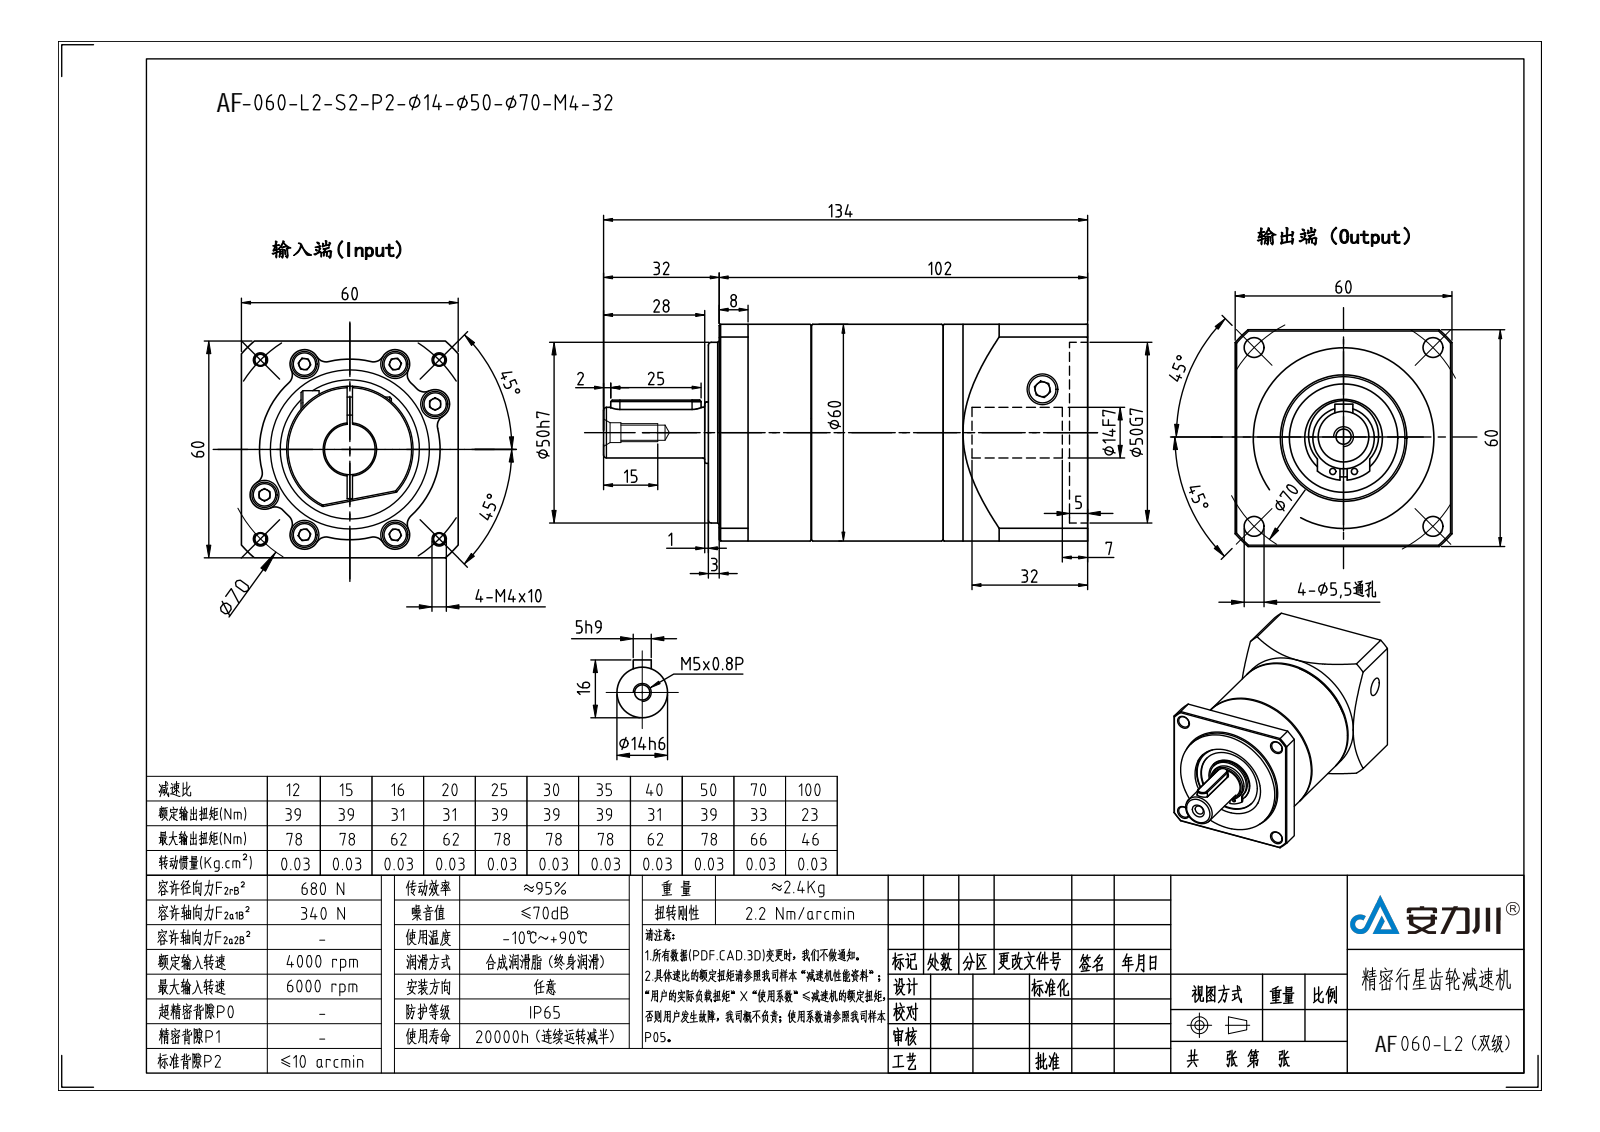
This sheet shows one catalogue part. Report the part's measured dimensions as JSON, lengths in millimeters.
{"part_name": "输入法兰PG060-50; PGA060-L2-14-50-70-M4-32; 输出端壳体PGA060; socket head cap screw_am_B18.3.1M - 5 x 0.8 x 20 Hex SHCS -- 20NHX (+6 more)", "step_written_by": "SolidWorks 2018 (CONFIG_CONTROL_DESIGN)", "units": "millimeters", "bodies": {"solids": 14, "faces": 530, "planar": 191, "cylindrical": 195, "other": 144}, "overall_size": [134, 60, 60], "volume_mm3": 253776, "surface_area_mm2": 68519, "round_holes": [[3.3, 10], [4.5, 6], [8, 6], [5.5, 4], [1.7, 2], [4.3, 2], [8.5, 1], [14, 1], [14.5, 1], [15.7, 1], [30, 1], [35, 1]], "round_bosses_or_shafts": [[7, 6], [4, 6], [60, 1], [47, 1], [24.5, 1], [21.5, 1], [20, 1], [17, 1]], "partial_cylinders_radius": [[3, 12], [0.5, 2], [2.5, 2], [4.5, 1], [9.7, 1], [11.65, 1], [40, 1]], "face_to_face_distances": [60, 36.5, 3, 1.5, 62, 20, 25.5, 40, 76.5, 102], "hole_center_spacings": [12.24, 26.75, 37.33, 49.88, 61.09, 35, 37.83, 49.5]}
